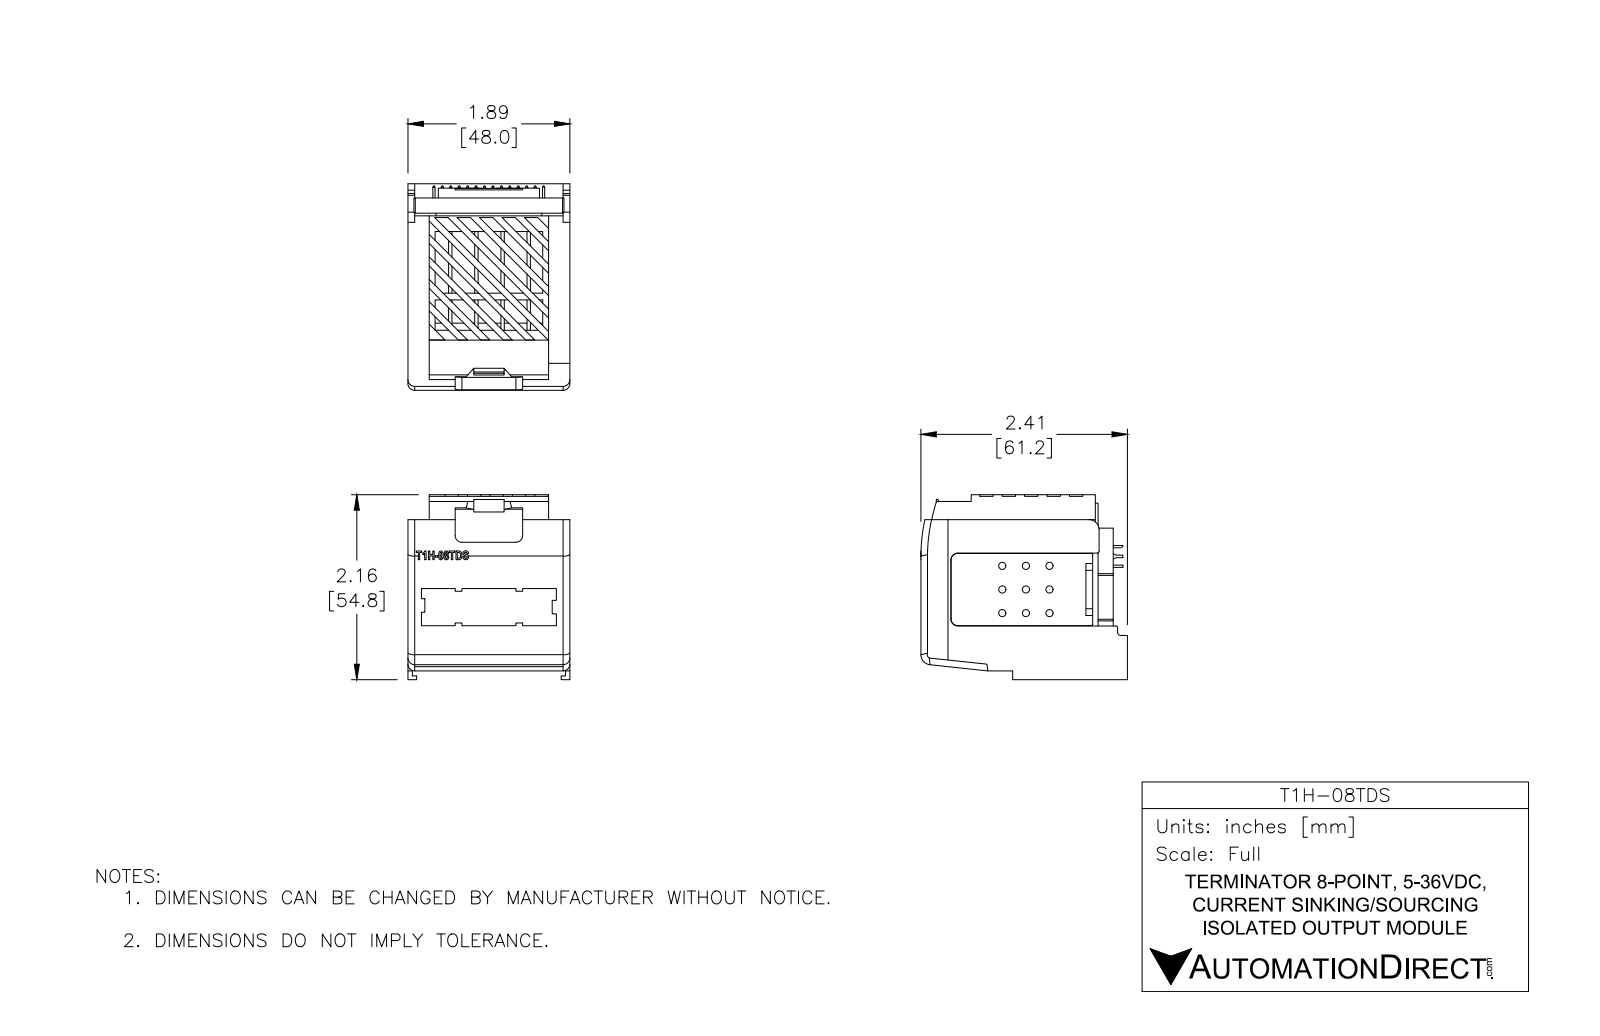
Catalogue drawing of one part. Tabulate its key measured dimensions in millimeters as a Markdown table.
| quantity | value |
| --- | --- |
| part name | T1H-08TDS |
| STEP written by | SolidWorks 2013 (AUTOMOTIVE_DESIGN) |
| units | millimeters |
| bodies | 1 solid, 659 faces (431 planar, 181 cylindrical, 47 other) |
| overall size | 88.7 × 65.1 × 61.36 |
| volume | 45 450 mm³ |
| surface area | 54 523 mm² |
| round holes (diameter × count) | 3 × 16 |
| round bosses / shafts (diameter × count) | 0.7 × 56 |
| partial cylindrical surfaces (radius × count) | 3.5 × 18, 1 × 5, 0.25 × 3, 0.55 × 3, 1.5 × 2, 8 × 1, 10 × 1, 18 × 1 |
| main face-to-face distances | 2, 86.7, 55.35, 0.5, 59.8, 88.7, 1.5, 55.26, 53.35, 84.7 |
| hole center spacings | 5.15, 10.3, 15.45, 20.6, 25.75, 30.9, 36.05, 41.2 |
